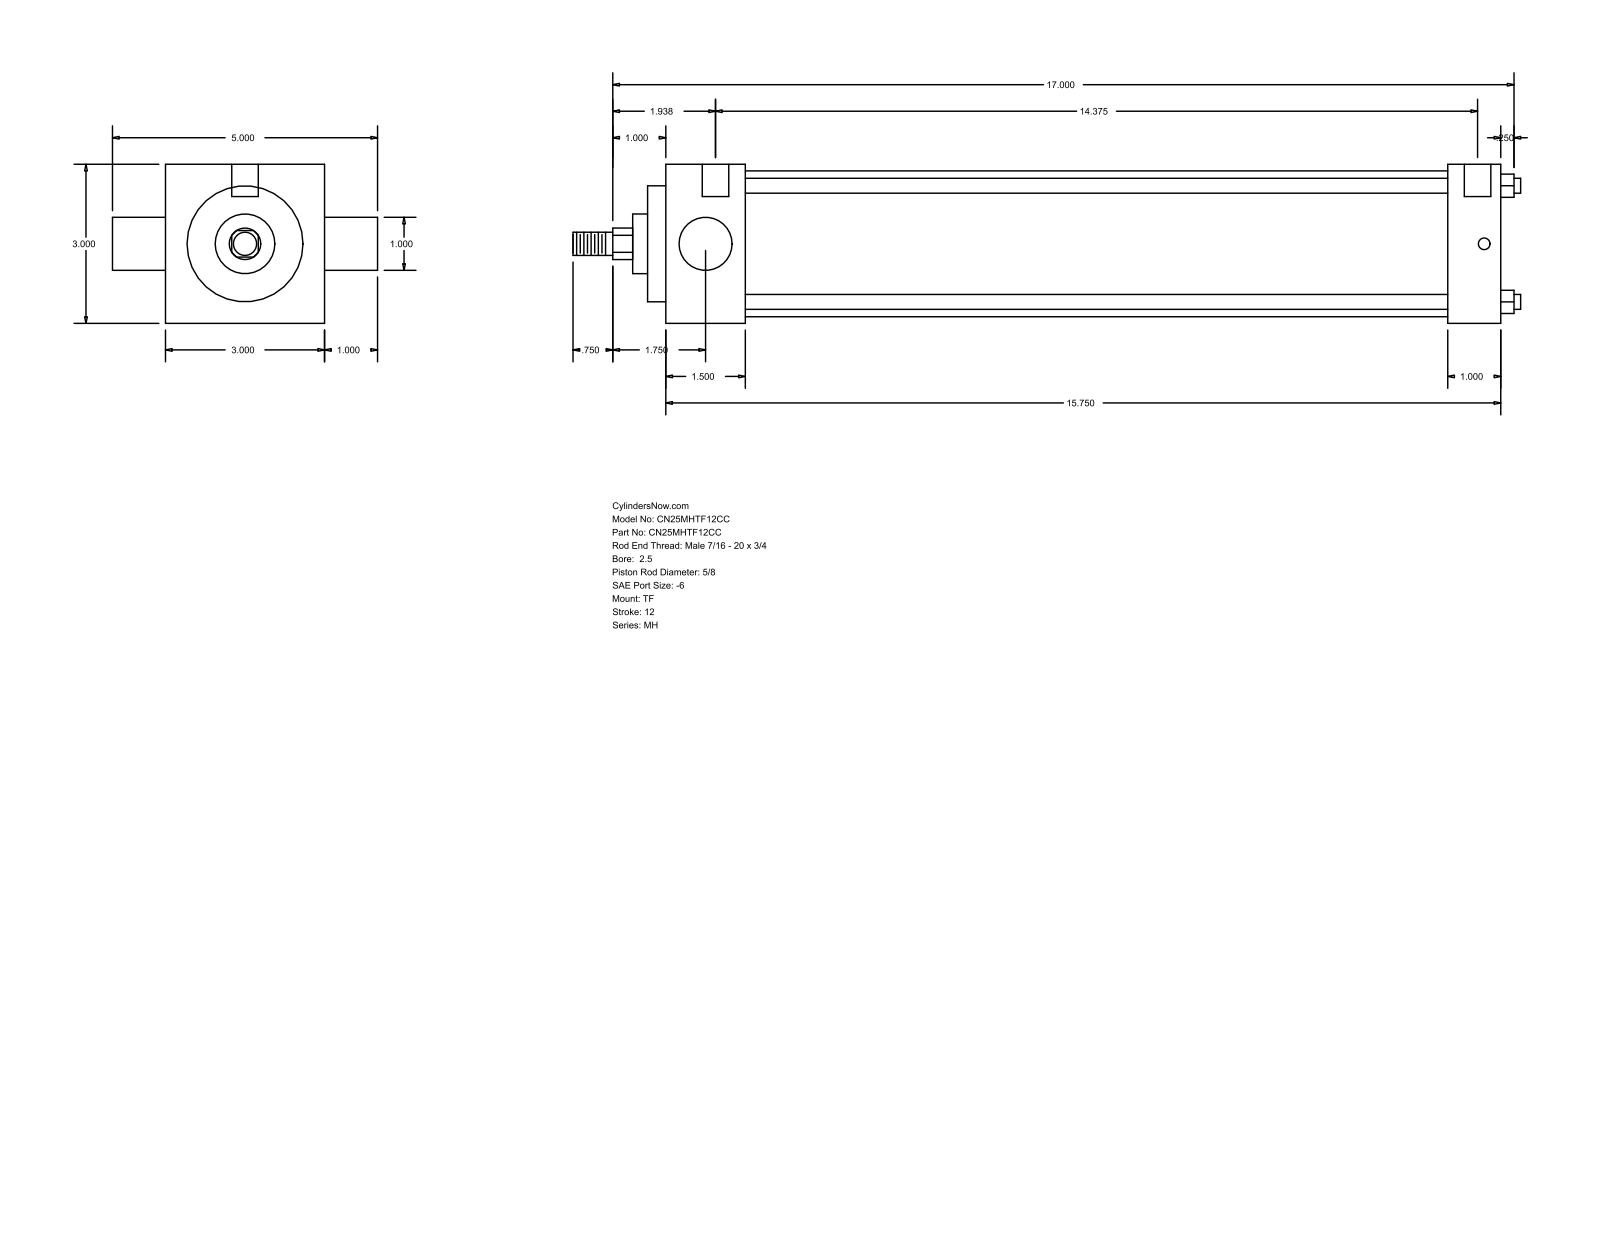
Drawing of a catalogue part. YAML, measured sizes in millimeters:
part_name: "MH_TF__0250_0.625"
step_written_by: "GSSL Pune (CONFIG_CONTROL_DESIGN)"
units: millimeters
bodies: {solids: 0, faces: 86, planar: 61, cylindrical: 25, other: 0}
overall_size: [454.02, 127, 76.2]
round_holes:
  - {diameter: 5.56, count: 3}
  - {diameter: 12.7, count: 2}
round_bosses_or_shafts:
  - {diameter: 7.14, count: 4}
  - {diameter: 69.85, count: 1}
  - {diameter: 55.55, count: 1}
  - {diameter: 28.57, count: 1}
  - {diameter: 25.4, count: 1}
  - {diameter: 15.88, count: 1}
  - {diameter: 11.11, count: 1}
partial_cylinders:
  - {radius: 7.54, count: 1}
face_to_face_distances: [76.2, 400.05, 25.4, 38.1, 361.95, 374.65, 336.55, 8.73, 46.83, 383.38]
hole_center_spacings: [3.17, 4.76, 365.13, 368.3, 369.89, 373.06]
